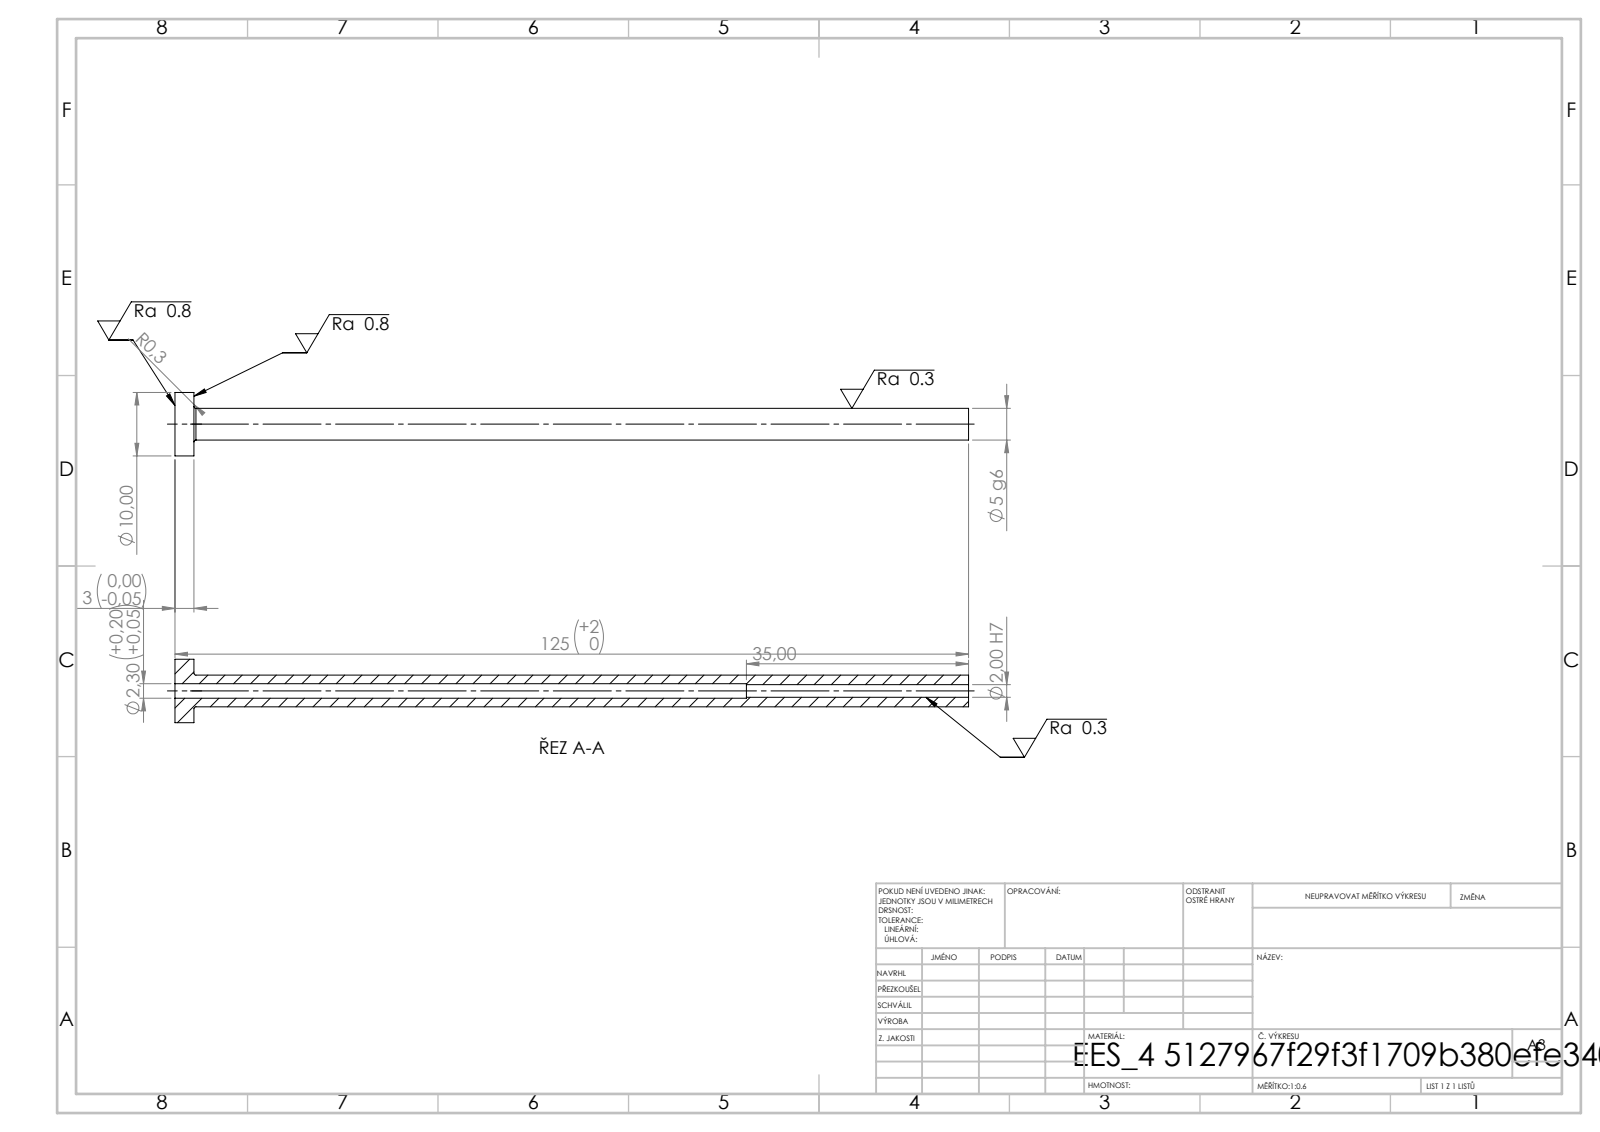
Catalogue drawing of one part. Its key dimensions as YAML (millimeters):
step_written_by: "SolidWorks 2019 (CONFIG_CONTROL_DESIGN)"
units: millimeters
bodies: {solids: 1, faces: 14, planar: 4, cylindrical: 8, other: 2}
overall_size: [125, 10, 10]
volume: 2148
surface_area: 3030
round_holes:
  - {diameter: 2, count: 1}
  - {diameter: 2.3, count: 1}
round_bosses_or_shafts:
  - {diameter: 10, count: 1}
  - {diameter: 5, count: 1}
face_to_face_distances: [3, 125, 122, 90, 87, 35]
